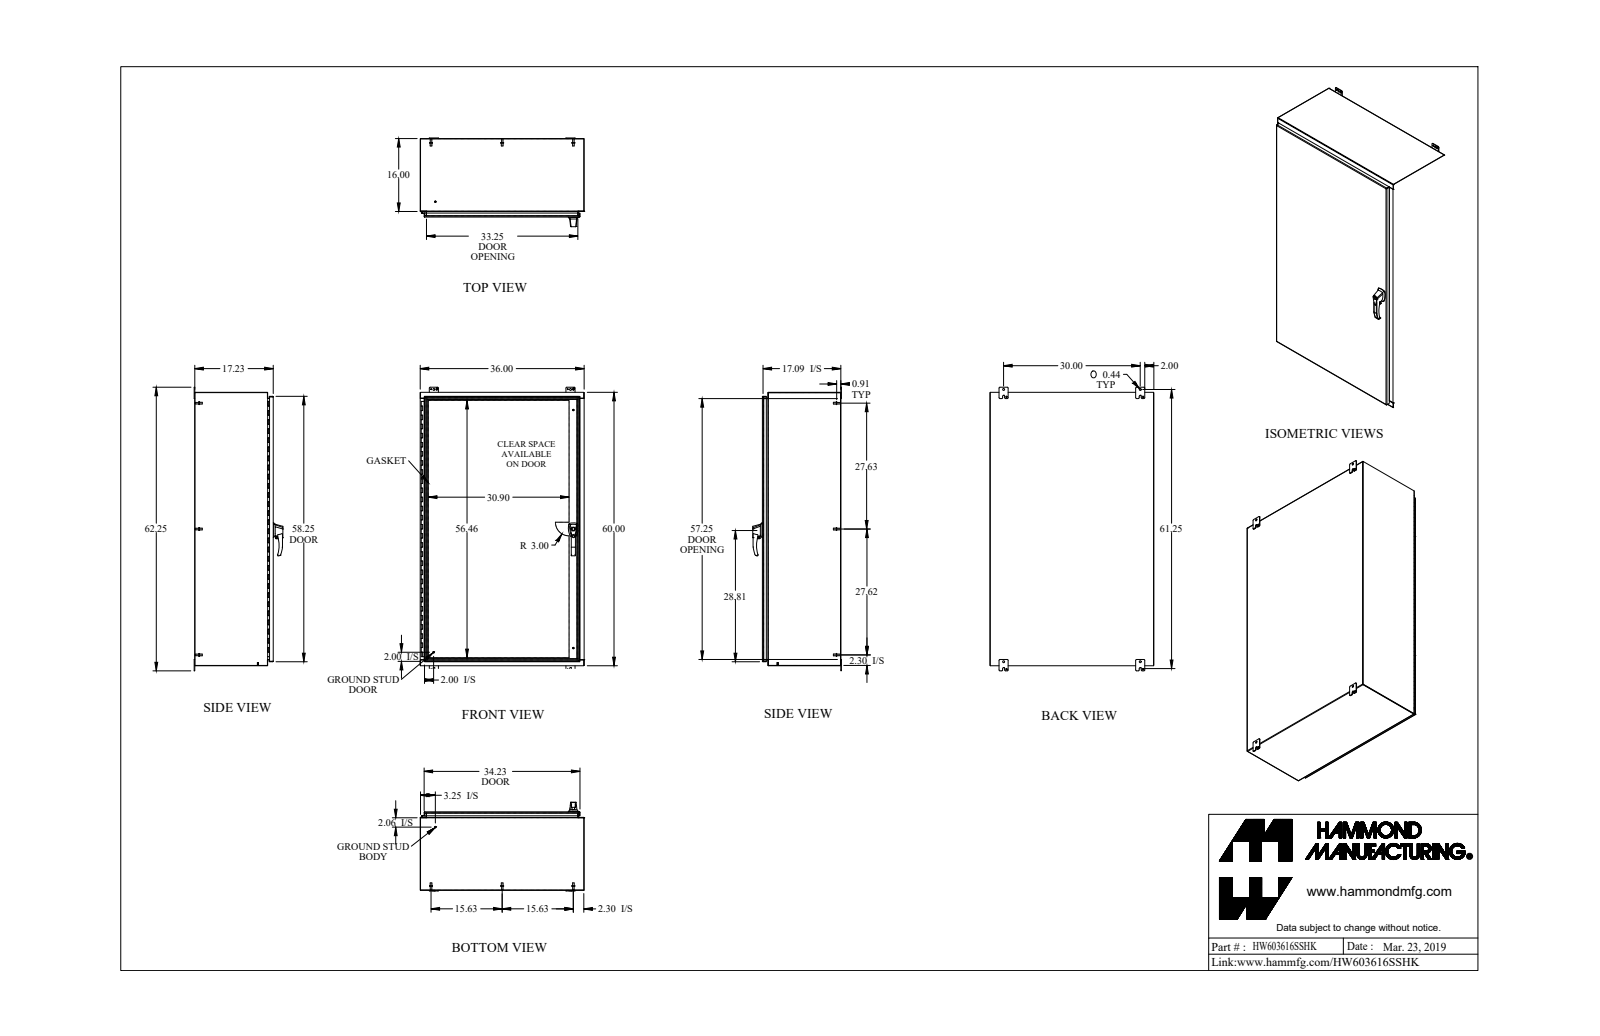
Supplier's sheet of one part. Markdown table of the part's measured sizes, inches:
| quantity | value |
| --- | --- |
| part name | HW603616SSHK |
| STEP written by | SolidWorks 2018 (AUTOMOTIVE_DESIGN) |
| units | inches |
| bodies | 52 solids, 1804 faces (905 planar, 761 cylindrical, 138 other) |
| overall size | 62.25 × 36 × 19.473 |
| volume | 665.6 in³ |
| surface area | 16 707 in² |
| round holes (diameter × count) | 0.313 × 7, 0.176 × 6, 0.437 × 4, 0.25 × 3, 0.265 × 3, 0.413 × 3, 0.196 × 2, 0.256 × 2, 0.394 × 2, 0.187 × 1, 0.233 × 1, 0.33 × 1 |
| round bosses / shafts (diameter × count) | 0.375 × 13, 0.65 × 8, 0.332 × 8, 0.25 × 7, 0.156 × 6, 1 × 3, 0.51 × 3, 0.313 × 3 |
| partial cylindrical surfaces (radius × count) | 0.25 × 27, 0.188 × 24, 0.036 × 14, 0.108 × 14, 0.06 × 12, 0.125 × 9, 0.218 × 8, 0.03 × 6 |
| main face-to-face distances | 0.072, 17.138, 17.066, 0.095, 17.233, 17.161, 35.928, 59.928, 35.856, 36 |
| hole center spacings | 1.736, 30, 59.75, 66.859, 26.118, 26.119, 52.237, 1.11 |
